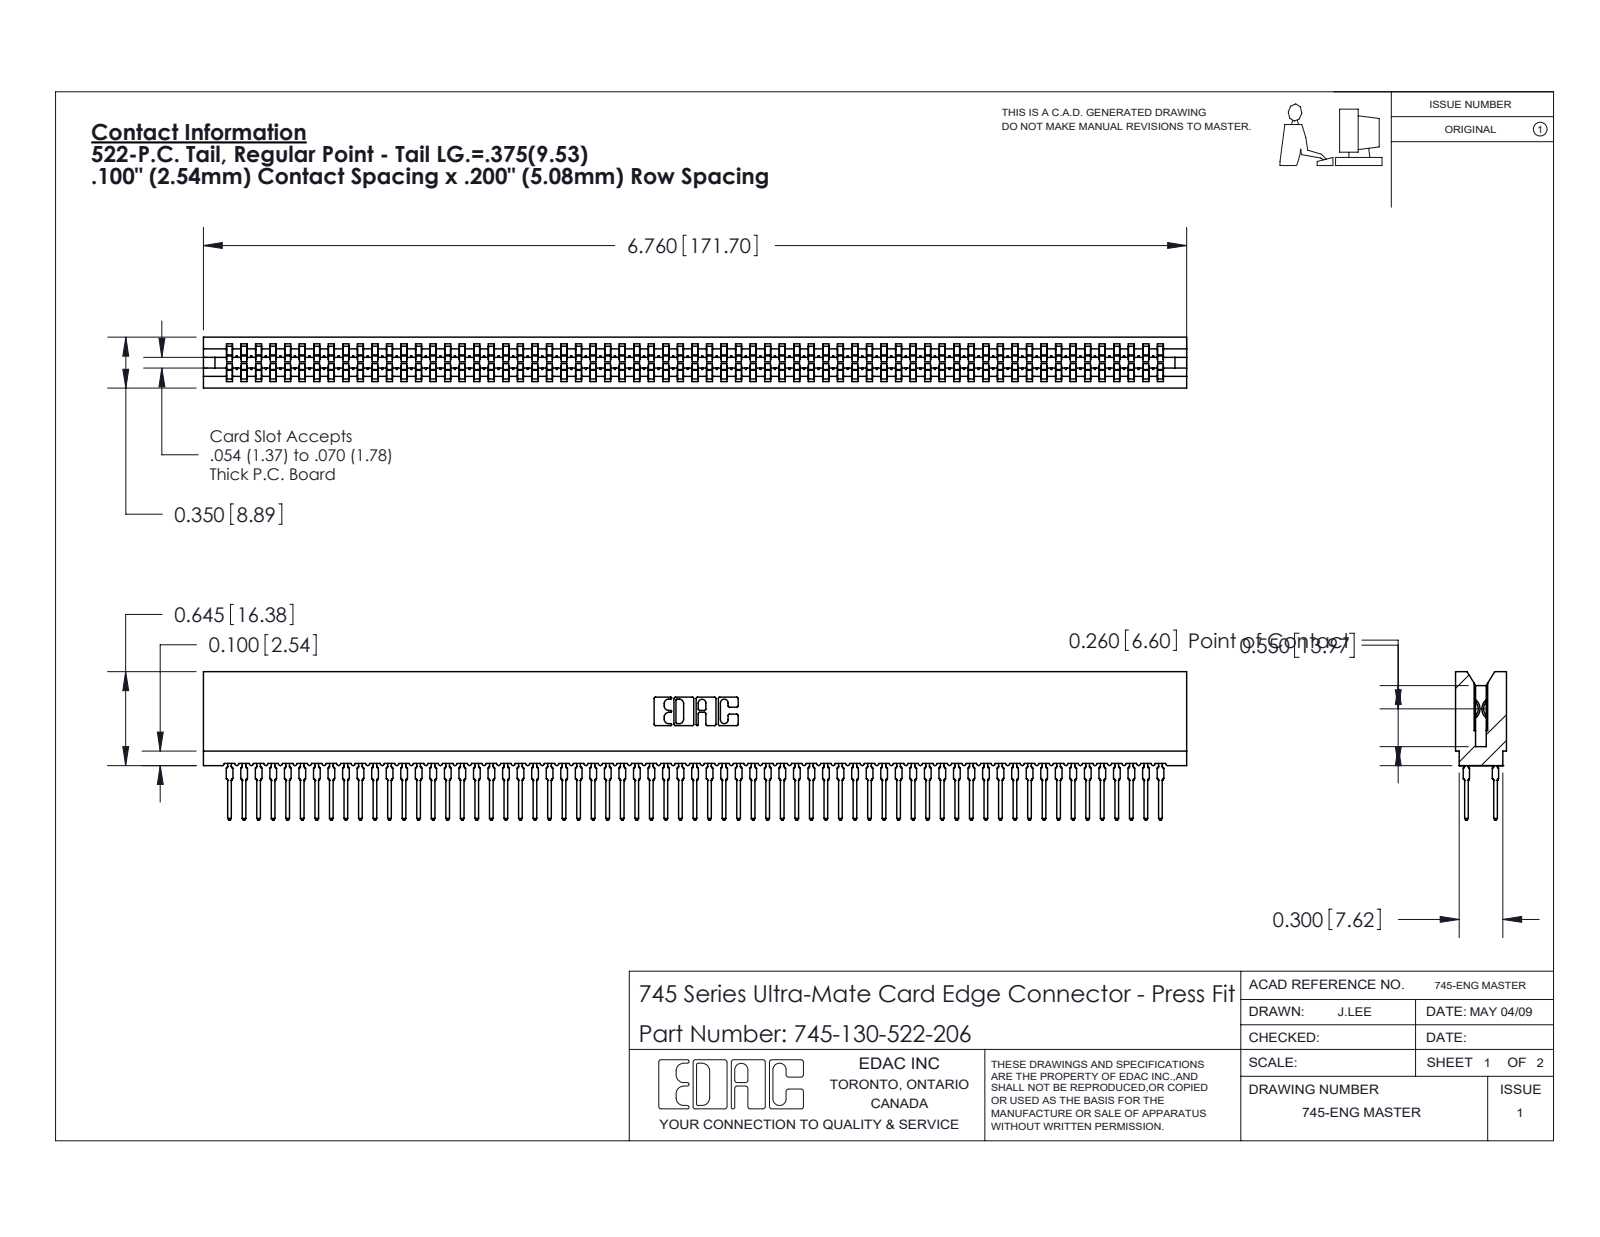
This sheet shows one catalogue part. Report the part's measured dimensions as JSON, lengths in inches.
{"part_name": "745 Part_Insulator Option - 06; 745-292-001_522; 745-130-522-206", "step_written_by": "SolidWorks 2020 (CONFIG_CONTROL_DESIGN)", "units": "inches", "bodies": {"solids": 131, "faces": 11731, "planar": 6036, "cylindrical": 2315, "other": 3380}, "overall_size": [6.76, 1.021, 0.35], "volume_in3": 0.942, "surface_area_in2": 50.22, "partial_cylinders_radius": [[0.021, 260], [0.015, 130], [0.01, 22], [0.005, 8], [0.011, 8], [0.007, 6], [0.031, 6], [0.026, 3]], "face_to_face_distances": [0.35, 0.063, 0.287, 0.045, 0.305, 0.018, 0.243, 0.138, 0.212, 0.093]}
